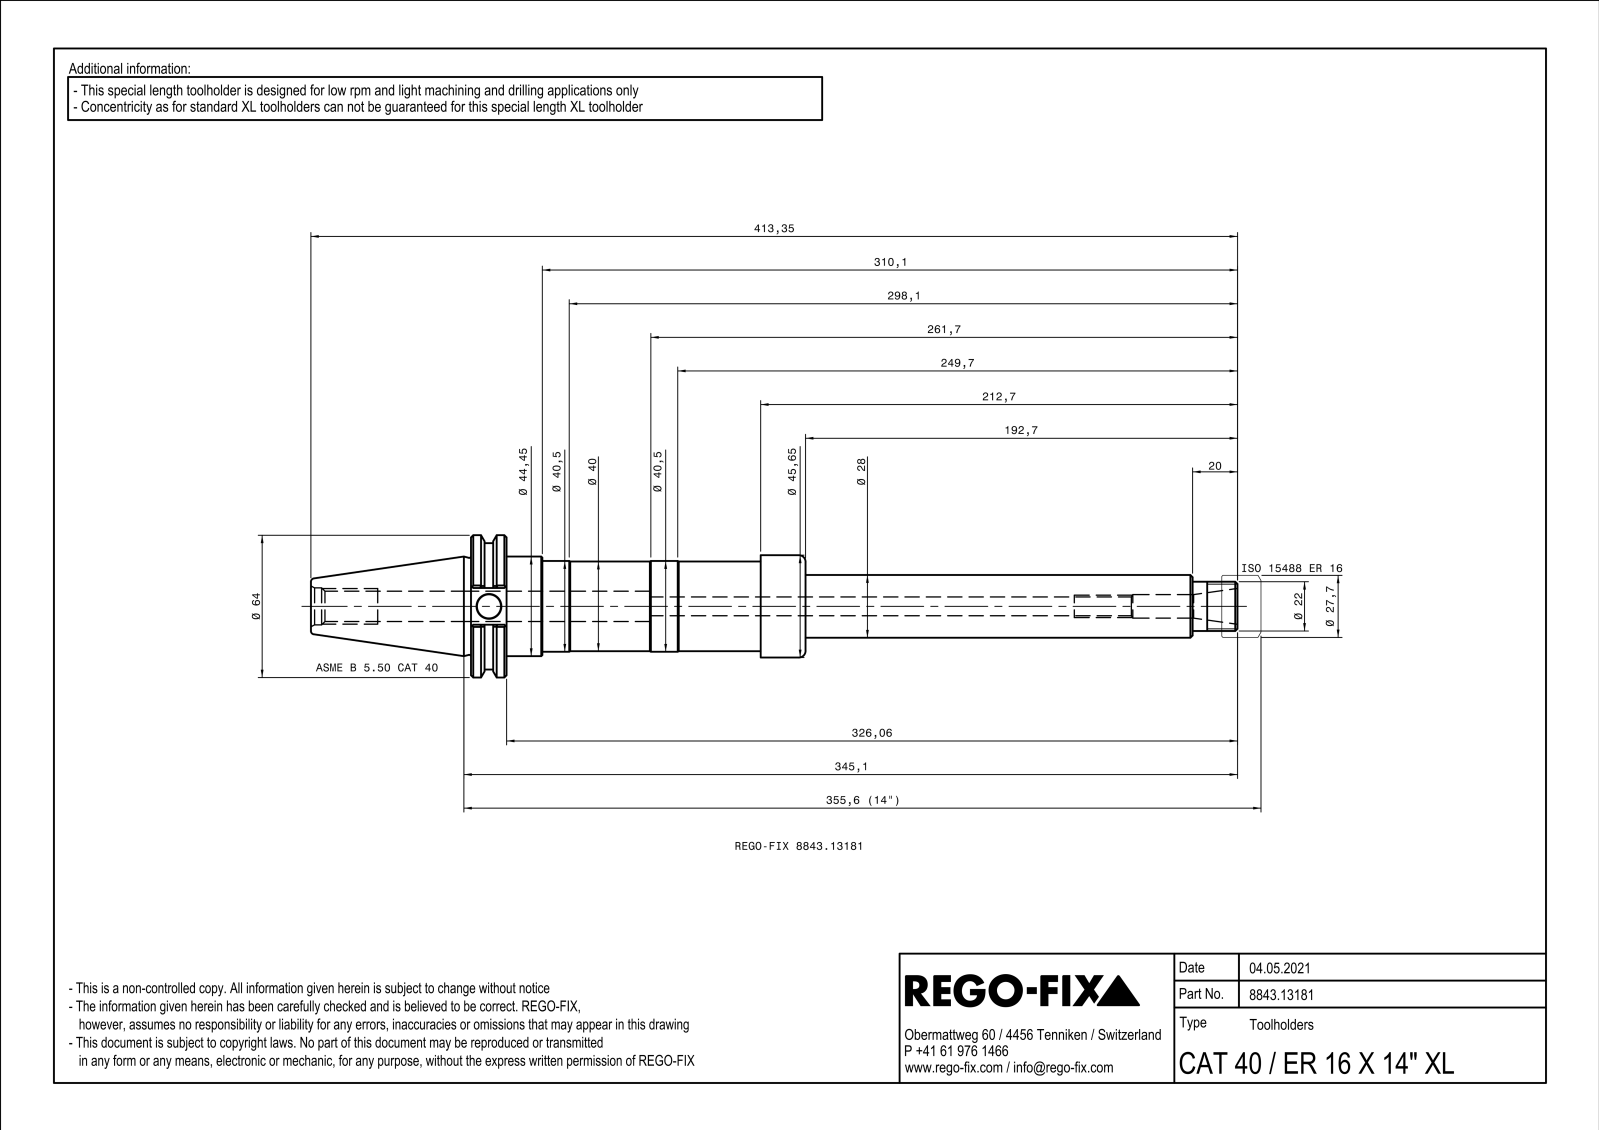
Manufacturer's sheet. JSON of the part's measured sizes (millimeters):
{"part_name": "NOCUT", "step_written_by": "SIEMENS PLM Software Solid Edge ST10 (AUTOMOTIVE_DESIGN)", "units": "millimeters", "bodies": {"solids": 1, "faces": 146, "planar": 42, "cylindrical": 34, "other": 70}, "overall_size": [413.35, 63.5, 60.79], "volume_mm3": 357771, "surface_area_mm2": 72326, "round_holes": [[8.35, 1], [8.38, 1], [10, 1], [10.5, 1], [10.7, 1], [13.53, 1], [16.5, 1], [25, 1], [29, 1], [38.38, 1], [40.05, 1], [43.3, 1]], "round_bosses_or_shafts": [[63.5, 1], [56.36, 1], [45.65, 1], [44.45, 1], [40.5, 1], [40, 1], [34, 1], [33, 1]], "partial_cylinders_radius": [[0.5, 4]], "face_to_face_distances": [15.87, 133.36, 149.23, 6, 14, 20, 1.5, 131.86, 147.73, 18.5]}
